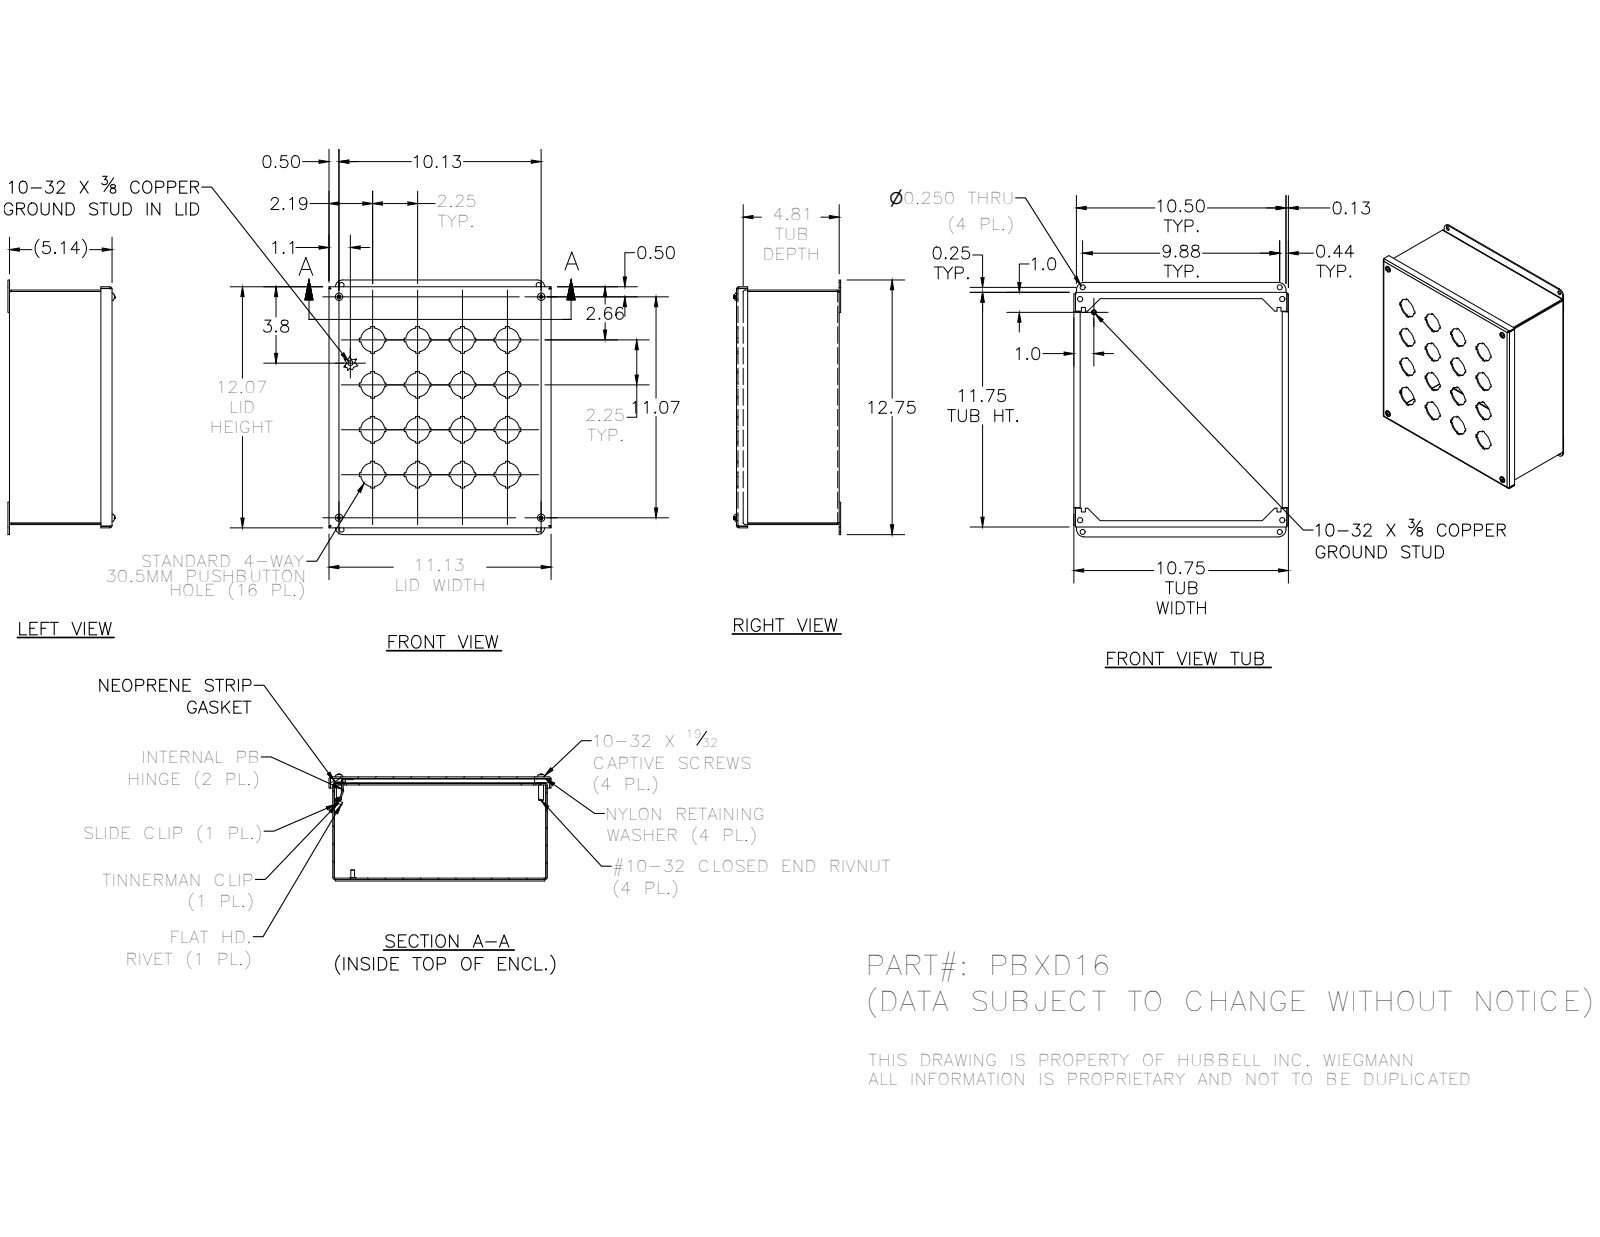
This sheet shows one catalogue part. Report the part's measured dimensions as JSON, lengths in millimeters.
{"part_name": "PBXD16LID; 372163; 39077; PBXD16BKP (+8 more)", "step_written_by": "Autodesk Inventor 2016 (AUTOMOTIVE_DESIGN)", "units": "millimeters", "bodies": {"solids": 25, "faces": 865, "planar": 555, "cylindrical": 196, "other": 114}, "overall_size": [323.85, 282.7, 135.79], "volume_mm3": 733266, "surface_area_mm2": 744242, "round_holes": [[30.48, 16], [3.96, 4], [4.98, 4], [6.35, 4], [6.53, 4], [7.06, 4], [7.14, 4], [7.94, 4], [3.56, 2]], "round_bosses_or_shafts": [[4.83, 6], [11.51, 4], [10.31, 4], [9.47, 4], [6.3, 4], [6.35, 3], [3.17, 1]], "partial_cylinders_radius": [[0.79, 12], [2.67, 12], [4.78, 6], [2.27, 4], [2.29, 4], [9.53, 4], [0.8, 3], [1.59, 3]], "face_to_face_distances": [1.88, 128.73, 130.61, 126.85, 271.17, 296.57, 273.05, 269.29, 298.45, 294.69], "hole_center_spacings": [57.15, 127.79, 80.82, 114.3, 180.72, 161.64, 171.45, 206.06]}
